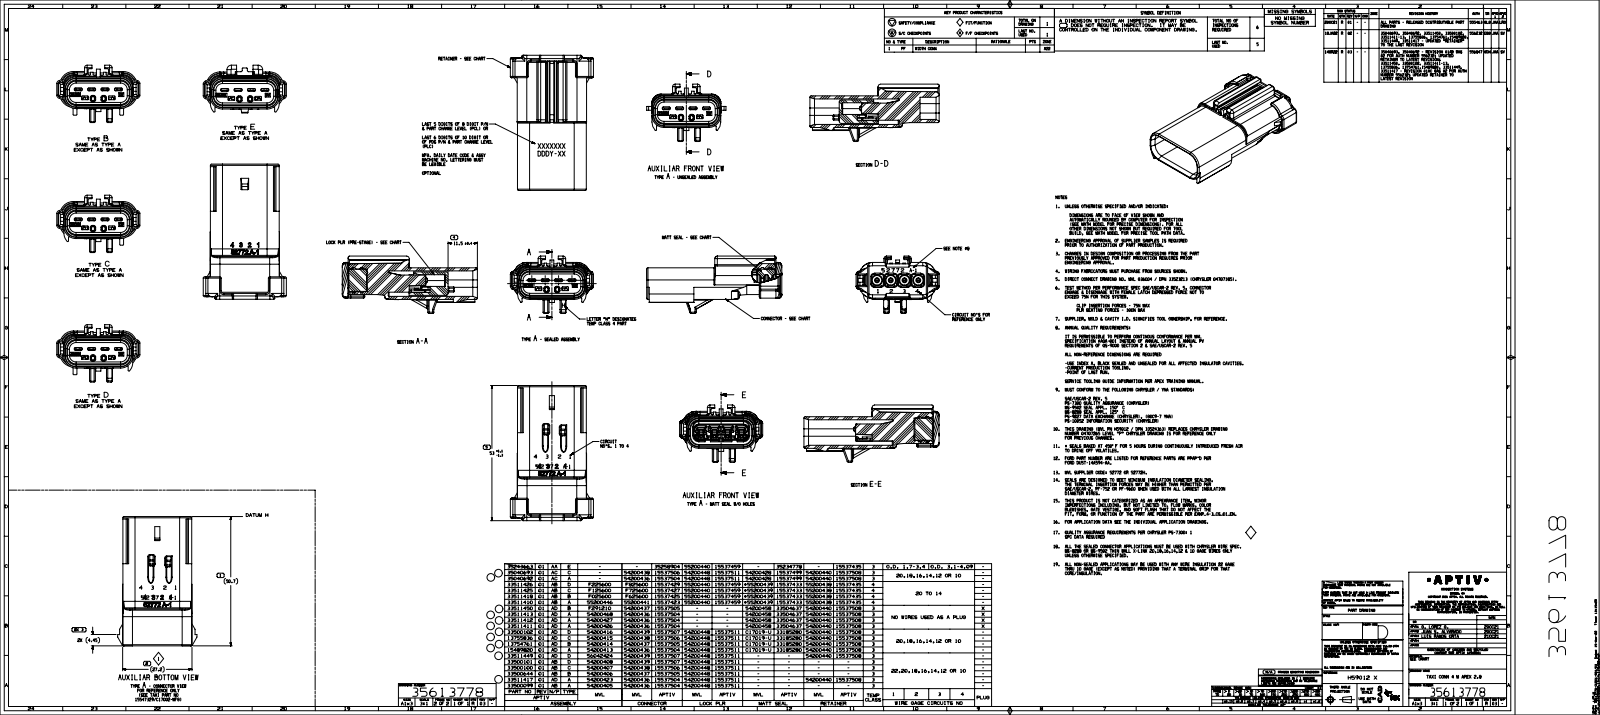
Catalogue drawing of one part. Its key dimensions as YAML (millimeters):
step_written_by: "SIEMENS PLM Software NX 9.0 (AP203_CONFIGURATION_CONTROLLED_3D_DESIGN_OF_MECHANICAL_PARTS_AND_ASSEMBLIES_MIM_LF)"
units: millimeters
bodies: {solids: 1, faces: 251, planar: 169, cylindrical: 54, other: 28}
overall_size: [53, 32.6, 22.51]
volume: 12949
surface_area: 9105
partial_cylinders:
  - {radius: 1, count: 7}
  - {radius: 4.75, count: 6}
  - {radius: 0.8, count: 4}
  - {radius: 1.2, count: 4}
  - {radius: 1.3, count: 4}
  - {radius: 3.4, count: 4}
  - {radius: 3.55, count: 4}
  - {radius: 3.75, count: 4}
face_to_face_distances: [11.2, 1.2, 10, 9.6, 1.91, 0.71, 10.8, 12.4, 1.6, 0.4]
